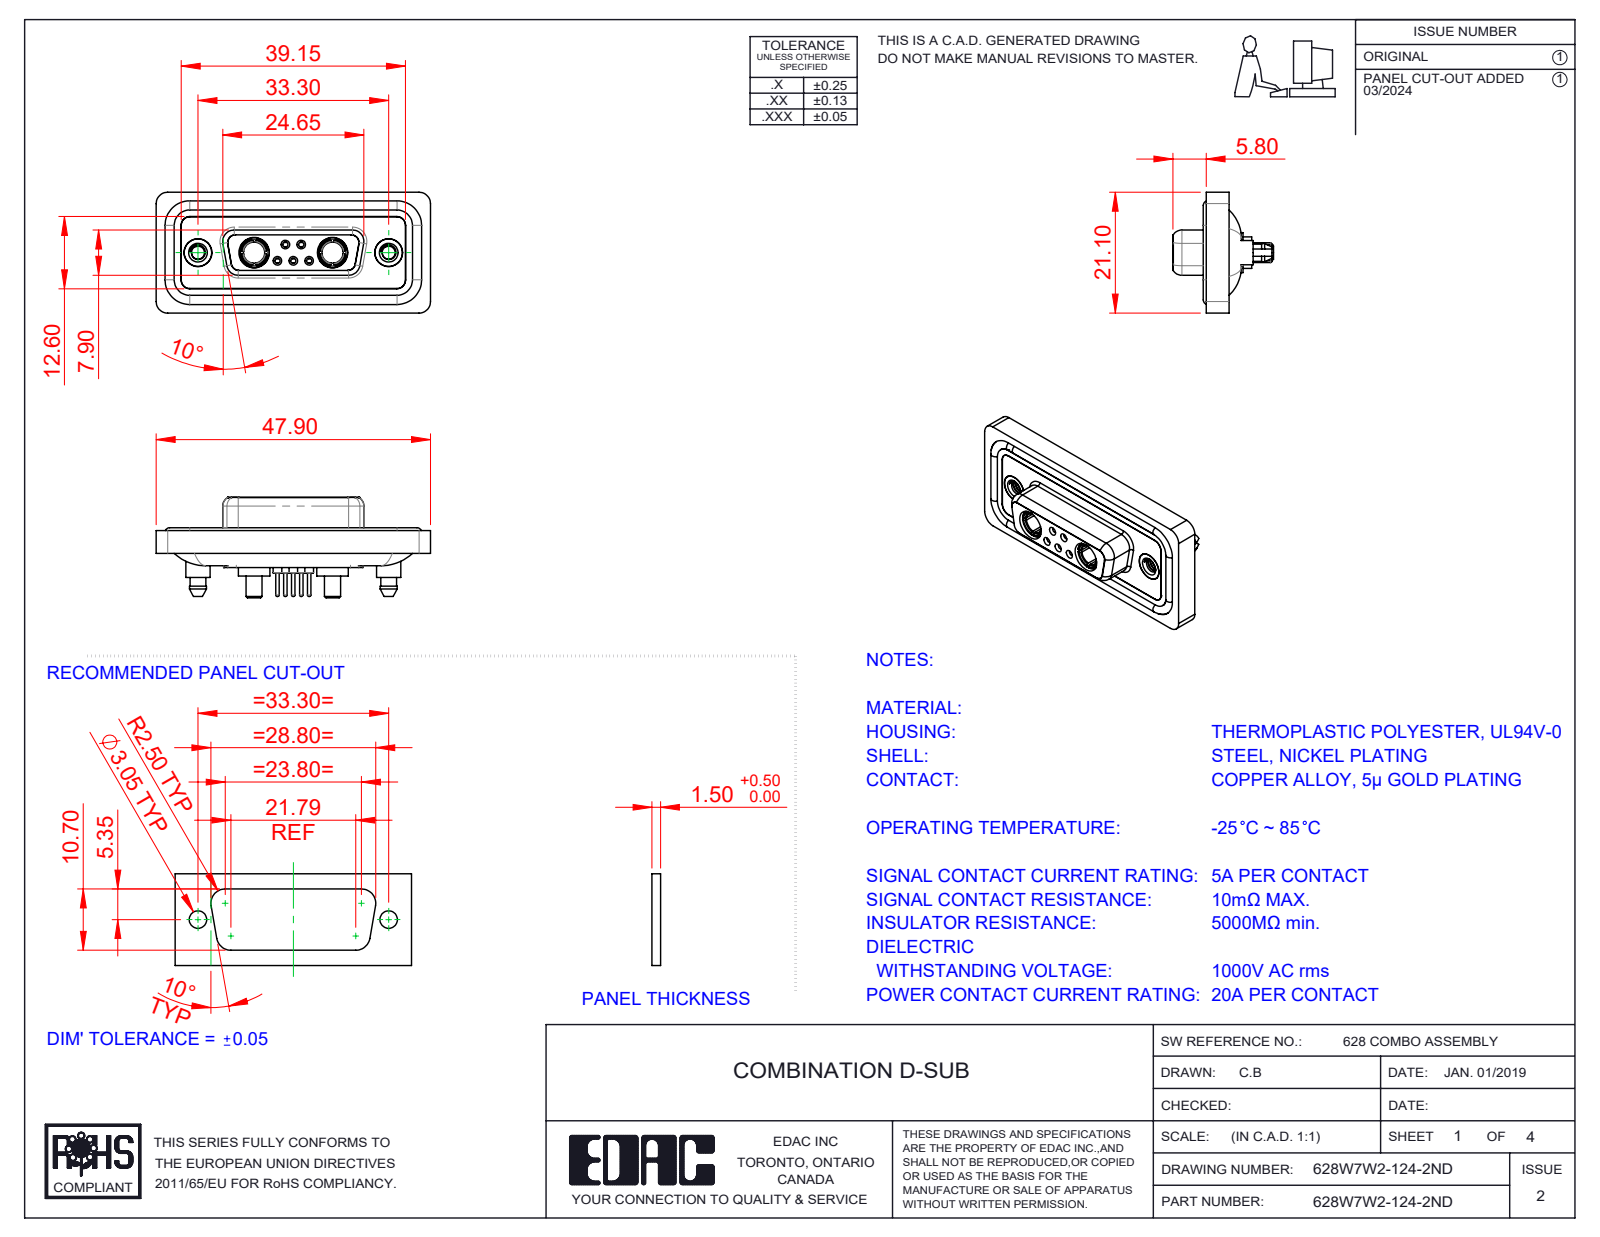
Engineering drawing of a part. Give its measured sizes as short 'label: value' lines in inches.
name: 628Combo Contact Row 1_24; Power Socket_20A S; 628Combo Waterproof Housing_15 Contacts; 628Combo Contact Row 2_24 (+5 more)
written by: SolidWorks 2023 (CONFIG_CONTROL_DESIGN)
unit: in
bodies: 16 solids, 875 faces (254 planar, 377 cylindrical, 244 other)
size: 1.886 × 0.831 × 0.691
volume: 0.379 in³; area: 15.85 in²
holes: 5× ⌀0.035, 5× ⌀0.043, 5× ⌀0.059, 5× ⌀0.079, 4× ⌀0.191, 3× ⌀0.063, 2× ⌀0.067, 2× ⌀0.089, 2× ⌀0.146, 2× ⌀0.157, 2× ⌀0.159, 2× ⌀0.197
bosses: 6× ⌀0.063, 5× ⌀0.087, 5× ⌀0.024, 2× ⌀0.217, 2× ⌀0.213, 2× ⌀0.205, 2× ⌀0.195, 2× ⌀0.195
rounds: 24× R0.059, 20× R0.079, 12× R0.053, 10× R0.063, 4× R0.01, 4× R0.02, 4× R0.024, 4× R0.026
face distances: 0.016, 0.071, 0.063, 0.02, 0.114, 0.043, 0.293, 0.222, 0.26, 0.278
hole spacings: 0.124, 0.109, 0.386, 0.925, 0.17, 0.17, 0.198, 0.198
